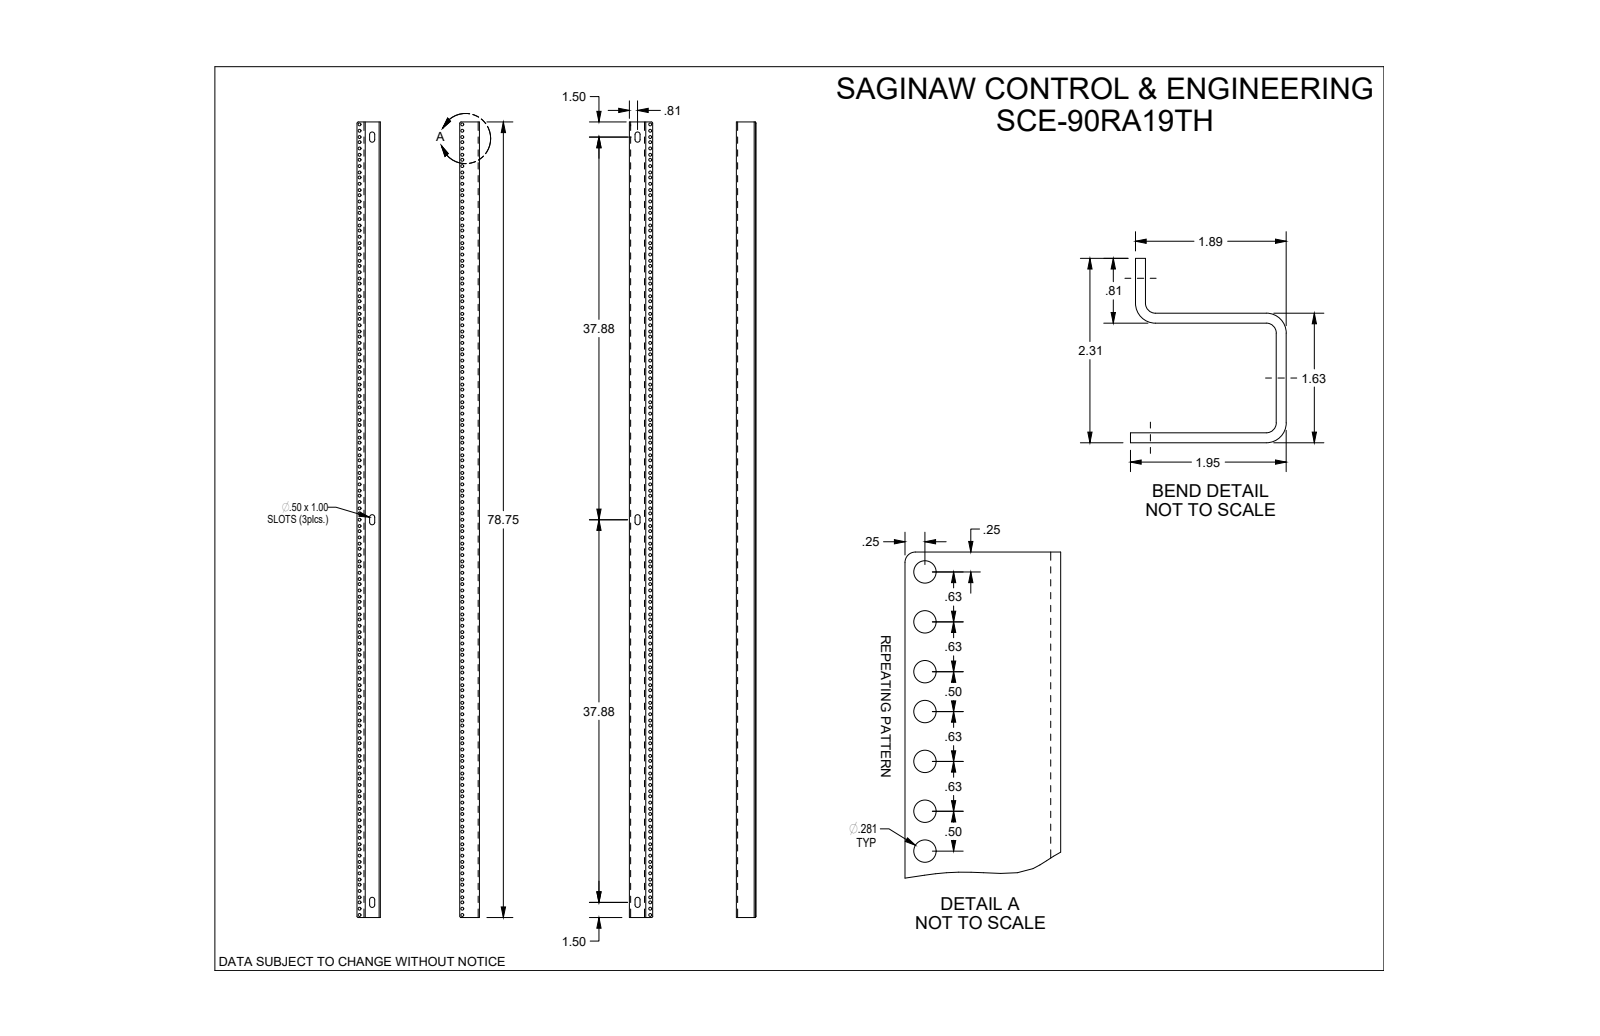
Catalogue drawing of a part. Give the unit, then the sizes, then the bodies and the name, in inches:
Units: inches
Overall size (bounding box): 78.75 × 21.719 × 2.312
Round holes (diameter × count): ⌀0.281 ×409
Partial cylindrical surfaces — rounded edges, fillets, slot ends (radius × count): R0.25 ×12, R0.125 ×8, R0.13 ×6
Main face-to-face distances: 0.125, 1.5, 1.625, 1.375, 0.125, 1.765, 19.828, 21.719, 21.594, 21.593
Hole centre spacings: 1.75, 3.5, 5.25, 7, 8.75, 0.625, 0.625, 1.25
Volume: 107 in³ · Surface area: 1 815 in²
Bodies: 2 solids, 608 faces (36 planar, 572 cylindrical, 0 other)
Part name (STEP PRODUCT): SCE-90RA19TH
STEP written by: SolidWorks 2019 (AUTOMOTIVE_DESIGN)
